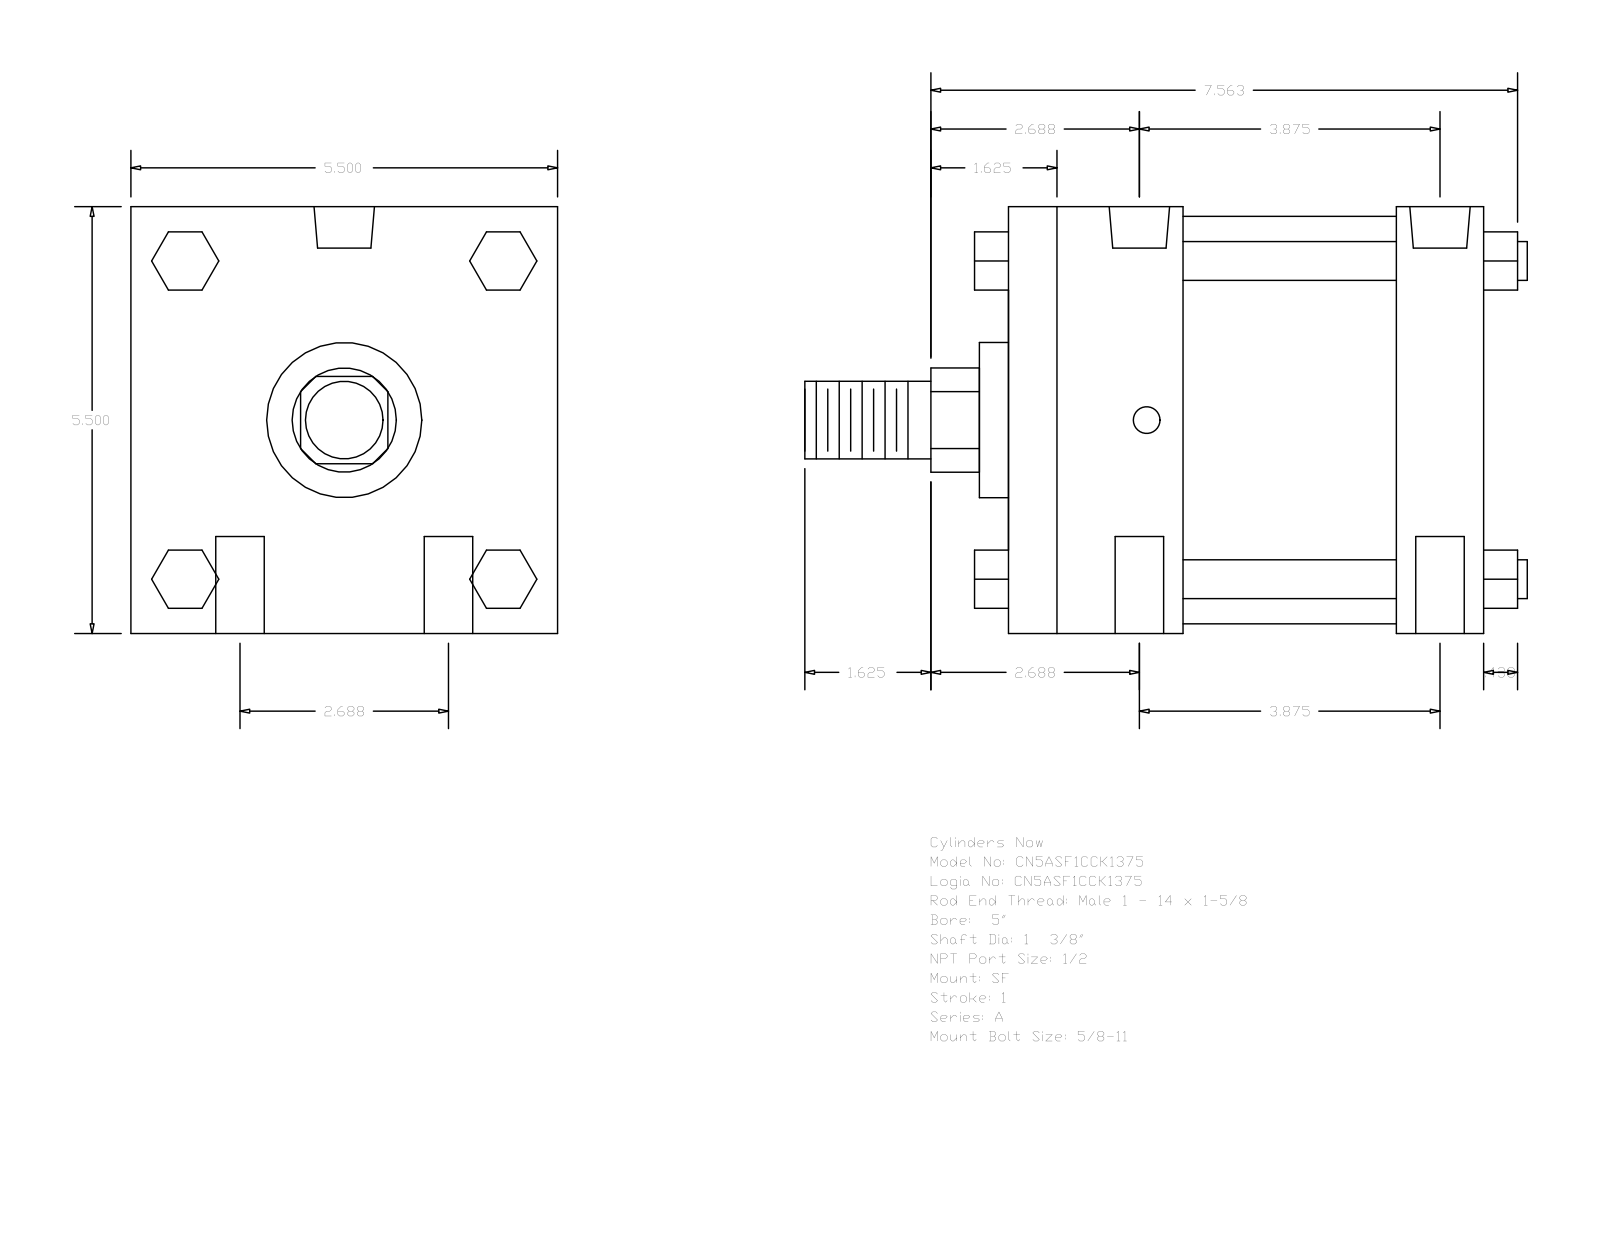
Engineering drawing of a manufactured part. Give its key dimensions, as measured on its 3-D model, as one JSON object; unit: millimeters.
{"part_name": "A_SF__0500_1.375", "step_written_by": "GSSL Pune (CONFIG_CONTROL_DESIGN)", "units": "millimeters", "bodies": {"solids": 0, "faces": 124, "planar": 94, "cylindrical": 30, "other": 0}, "overall_size": [236.54, 139.7, 139.7], "round_holes": [[15.88, 4], [8.73, 2], [19.77, 2]], "round_bosses_or_shafts": [[12.7, 4], [133.35, 1], [50.8, 1], [34.92, 1], [25.4, 1]], "partial_cylinders_radius": [[17.06, 1]], "face_to_face_distances": [139.7, 155.57, 127, 57.15, 69.85, 98.42, 28.57, 19.05, 52.07, 90.18], "hole_center_spacings": [34.13, 104.18, 98.43, 68.26, 119.78, 93.65]}
